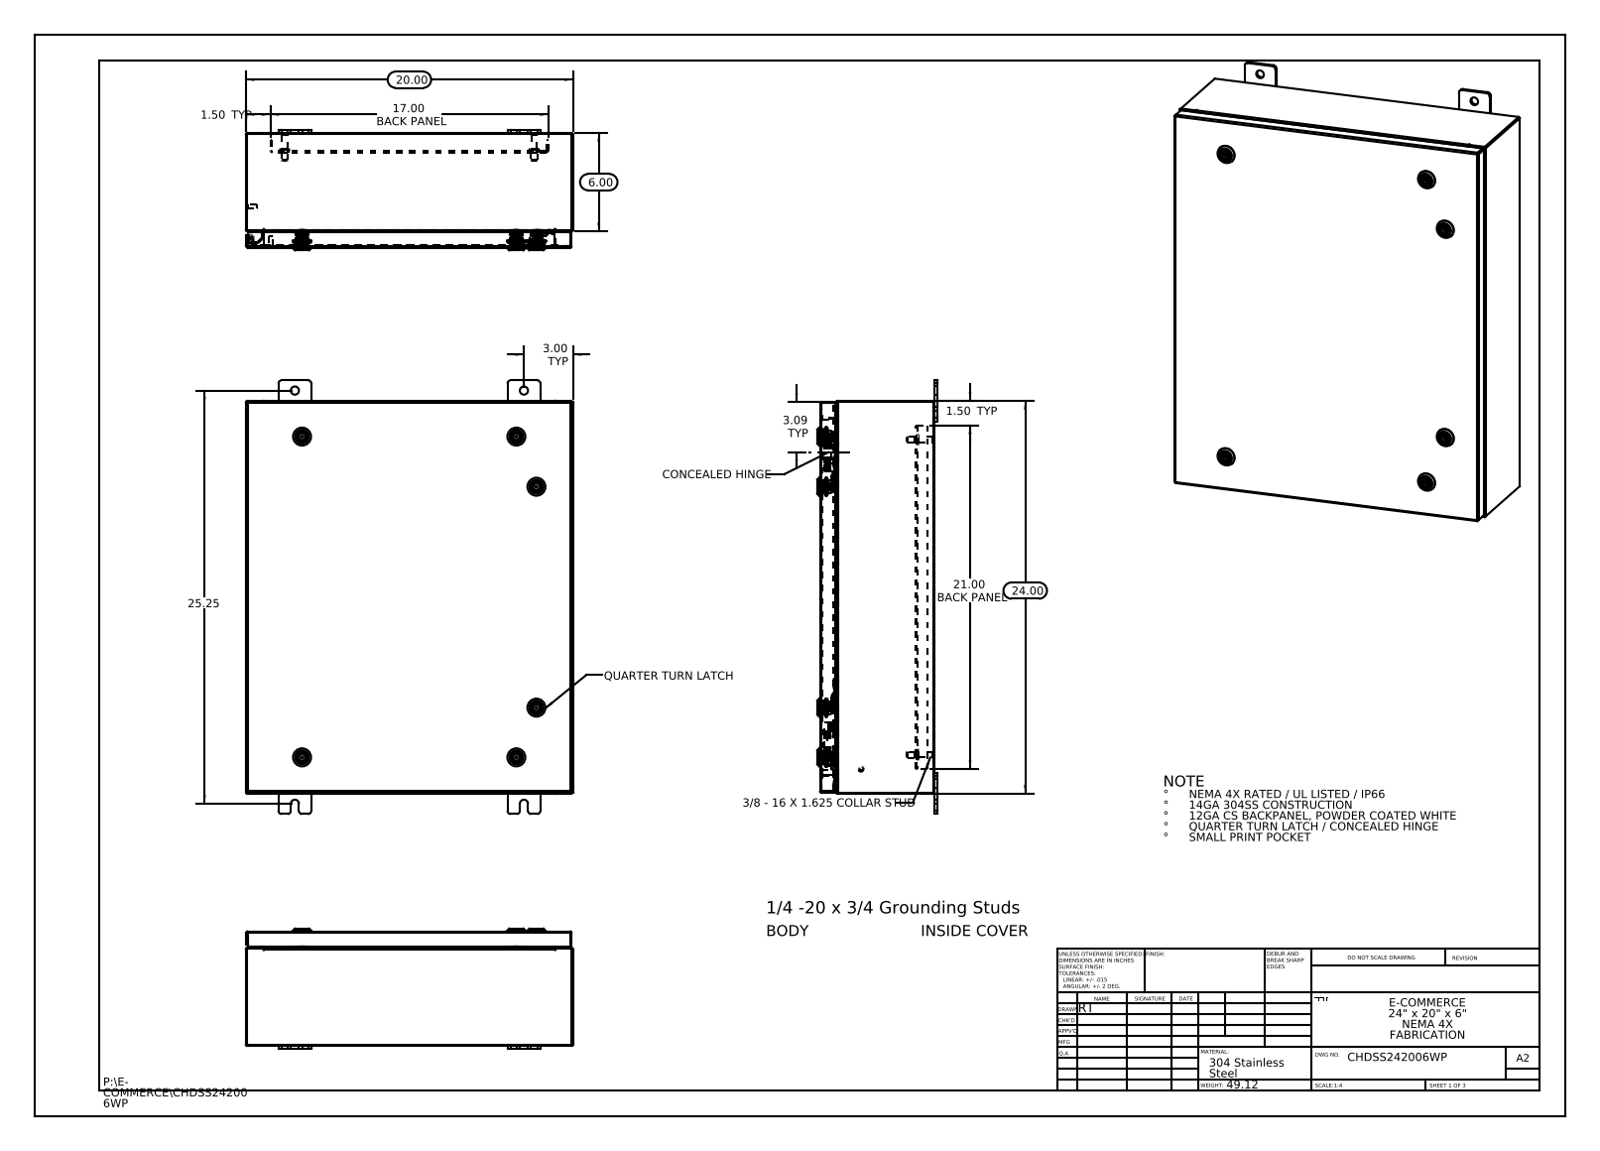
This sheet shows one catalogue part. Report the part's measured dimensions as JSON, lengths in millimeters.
{"part_name": "Screw-221320-IB-Industrilas_Screw-221320-IB-Industrilas; Housing-211301-IB-Industrilas_Housing-211301-IB-Industrilas; HW-CLH-E5-8004_Cam-232112-U-Industrilas; CHDSS242006WP Top (+8 more)", "step_written_by": "SolidWorks 2013 (CONFIG_CONTROL_DESIGN)", "units": "millimeters", "bodies": {"solids": 55, "faces": 5420, "planar": 1592, "cylindrical": 1692, "other": 2136}, "overall_size": [75802.9, 59112.8, 186.8], "volume_mm3": 2886000, "surface_area_mm2": 2823000, "round_holes": [[12.7, 8], [5, 6], [10, 6], [10.2, 6], [16, 6], [20, 6], [3.5, 4], [5.4, 2]], "round_bosses_or_shafts": [[6, 8], [28, 6], [19.8, 6], [15.9, 6], [15.5, 6], [13.5, 6], [10, 6], [2.9, 6]], "partial_cylinders_radius": [[0.2, 198], [3, 198], [0.7, 72], [0.5, 24], [4.8, 24], [5, 24], [0.3, 20], [2.2, 18]], "face_to_face_distances": [1.9, 1.9, 178.1, 176.1, 176.2, 174.3, 2.6, 25.4, 27.3, 148.9], "hole_center_spacings": [47.2, 73.1, 77.9, 332.7, 355.6, 387.4, 397.6, 416]}
